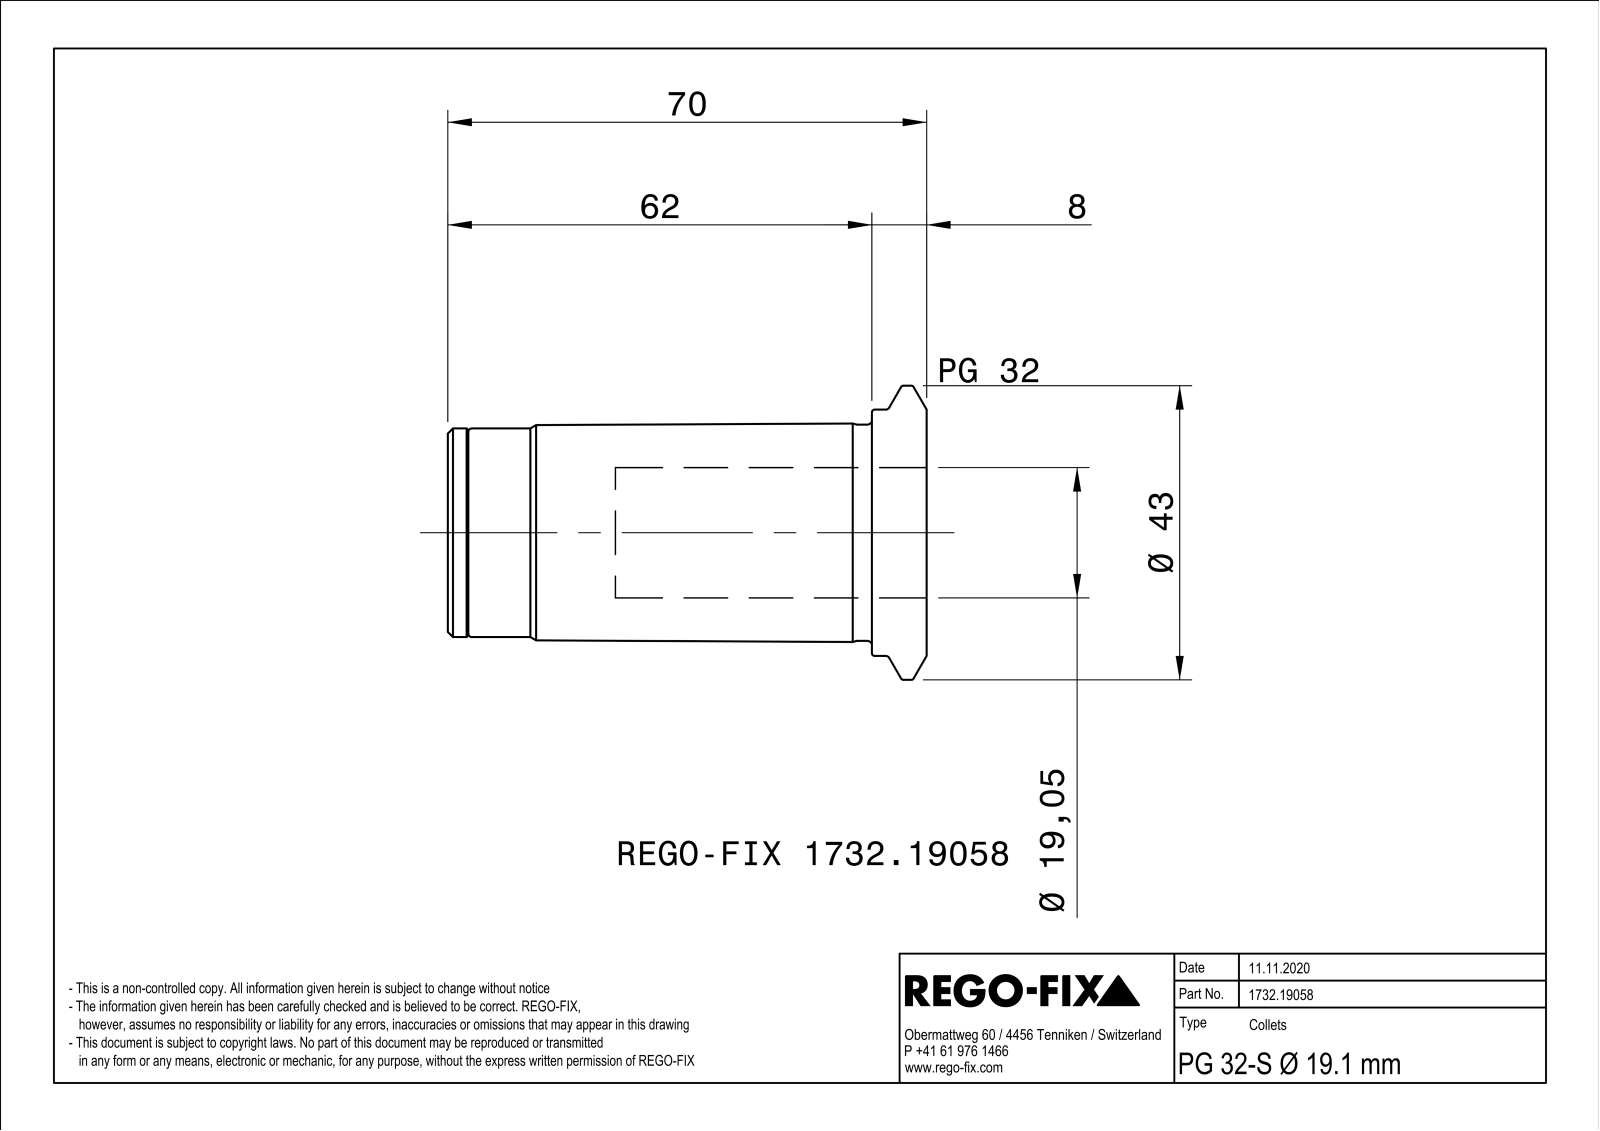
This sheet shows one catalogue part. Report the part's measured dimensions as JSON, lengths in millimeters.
{"part_name": "NOCUT", "step_written_by": "SIEMENS PLM Software Solid Edge ST10 (AUTOMOTIVE_DESIGN)", "units": "millimeters", "bodies": {"solids": 1, "faces": 84, "planar": 21, "cylindrical": 21, "other": 42}, "overall_size": [70, 43, 42.99], "volume_mm3": 36810, "surface_area_mm2": 16209, "round_holes": [[4, 3], [8.92, 1], [19.05, 1], [25.6, 1], [26.92, 1], [28.5, 1]], "round_bosses_or_shafts": [[43, 1], [36, 1], [31.6, 1], [30.5, 1], [26.5, 1]], "face_to_face_distances": [1, 70, 9, 61, 3, 8, 53, 62, 58, 50], "hole_center_spacings": [7.75, 13.43, 13.42]}
